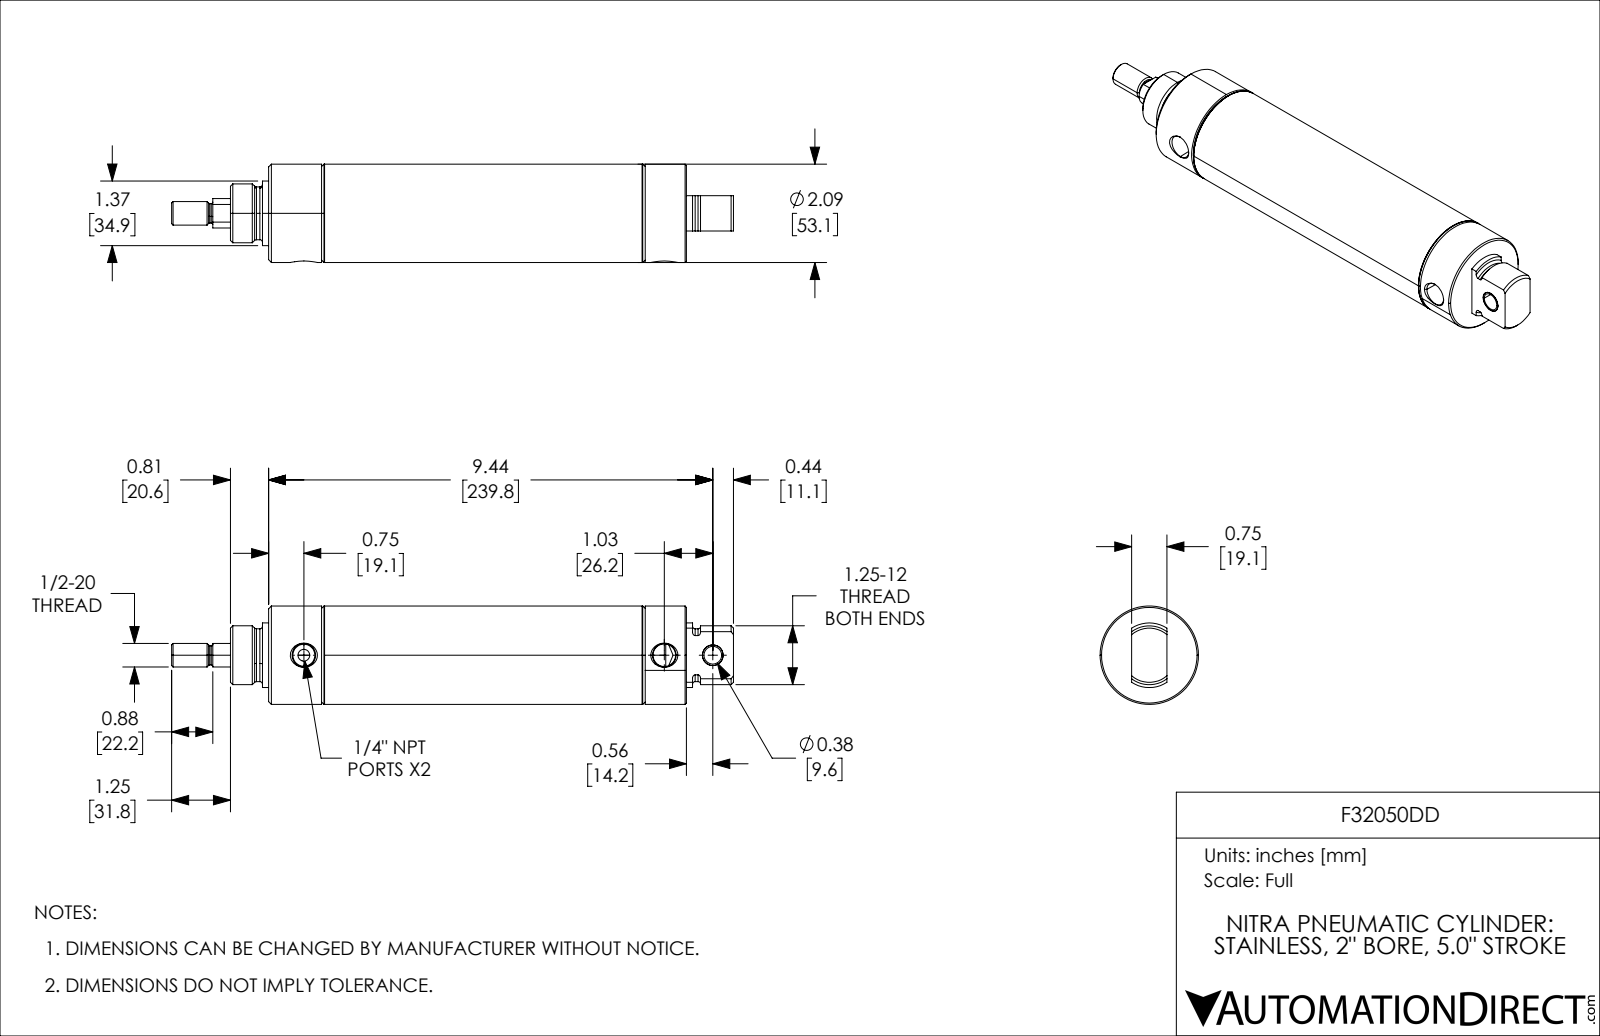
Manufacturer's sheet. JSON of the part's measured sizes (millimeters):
{"part_name": "F32050DD; F32050DD_9; F32050DD_5; F32050DD_11 (+2 more)", "step_written_by": "SolidWorks 2021 (CONFIG_CONTROL_DESIGN)", "units": "millimeters", "bodies": {"solids": 5, "faces": 160, "planar": 31, "cylindrical": 60, "other": 69}, "overall_size": [303.23, 53.09, 53.09], "volume_mm3": 280970, "surface_area_mm2": 109977, "round_holes": [[6.35, 1], [9.55, 1], [11.15, 1], [12.18, 1], [16.52, 1], [19.05, 1], [49.05, 1]], "round_bosses_or_shafts": [[53.09, 1], [51.16, 1], [34.87, 1], [31.75, 1], [28.51, 1], [15.88, 1], [12.7, 1], [10.46, 1]], "partial_cylinders_radius": [[14.25, 1]], "face_to_face_distances": [30.18, 127, 157.18, 187.4, 60.4, 30.22, 38.15, 165.15, 195.33, 225.55], "hole_center_spacings": [26.17, 194.56, 220.73]}
